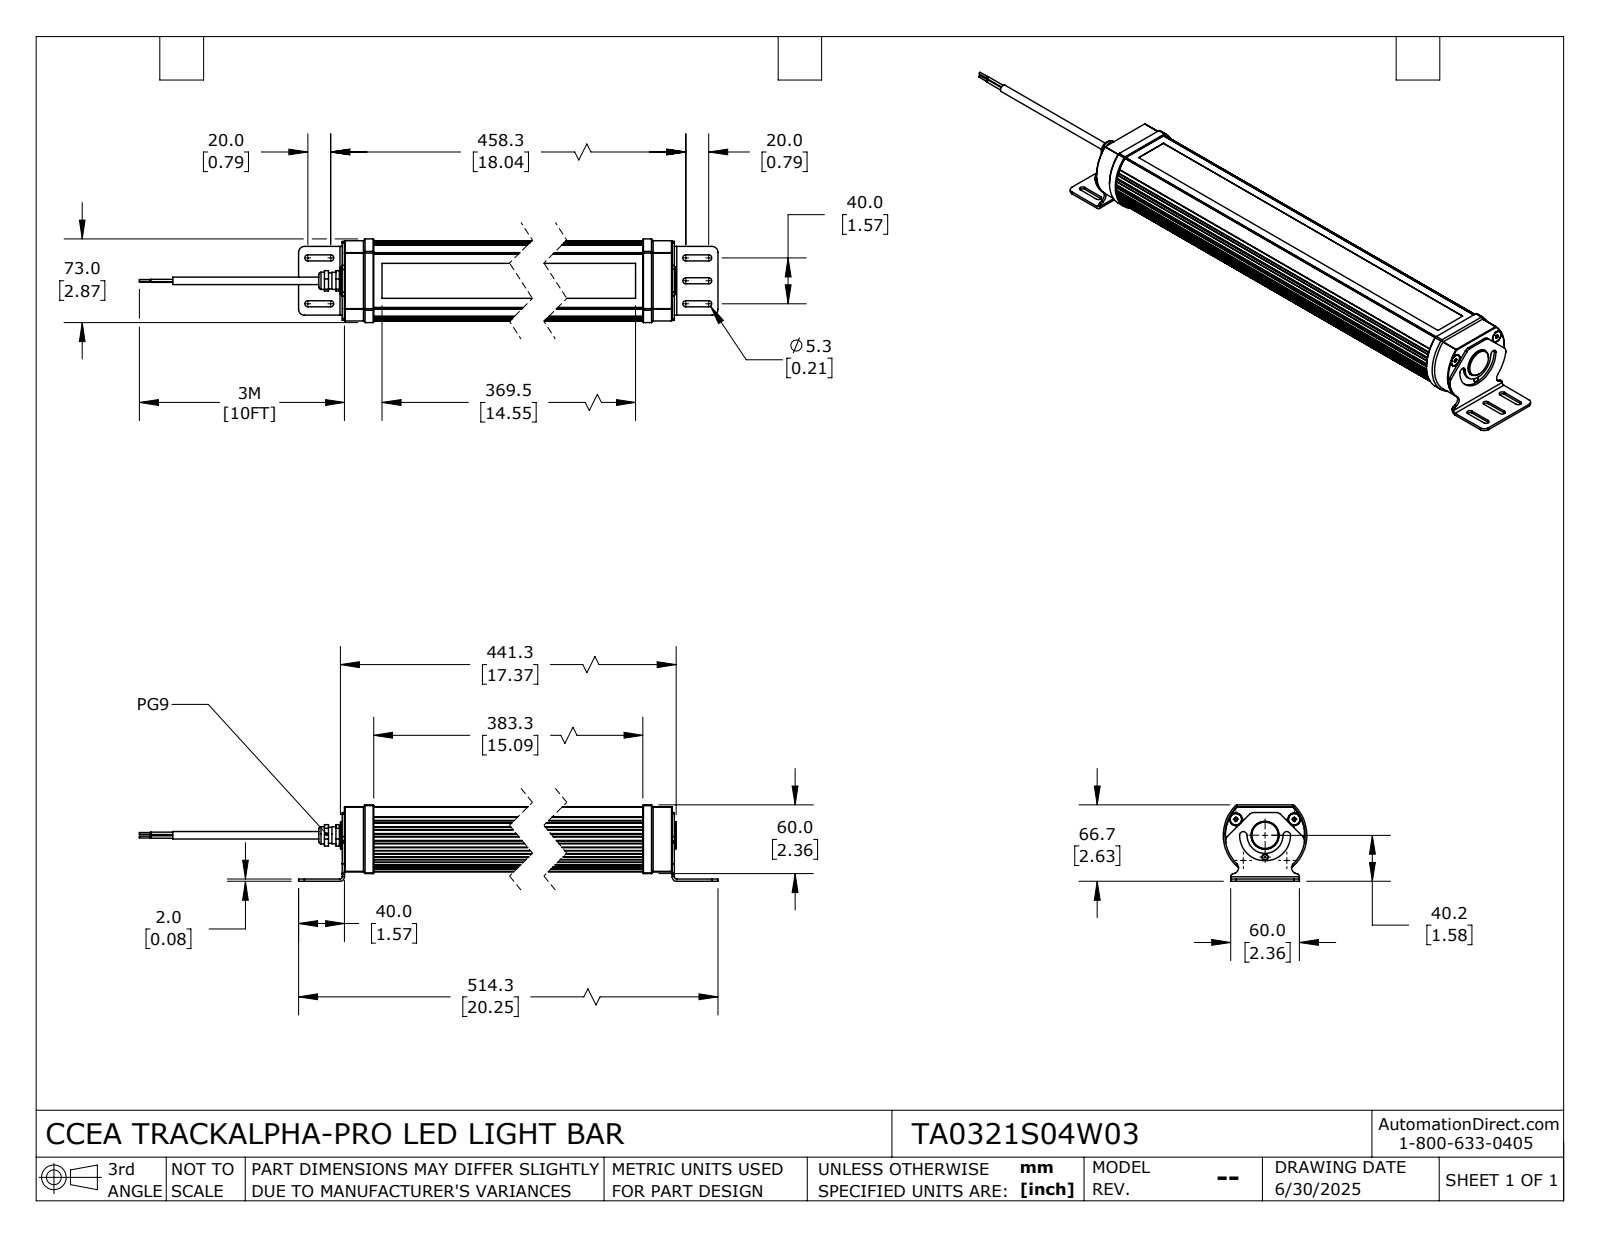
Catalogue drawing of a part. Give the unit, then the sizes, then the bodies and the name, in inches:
Units: inches
Overall size (bounding box): 25.72 × 2.874 × 2.626
Round holes (diameter × count): ⌀0.217 ×4, ⌀0.043 ×2, ⌀0.12 ×2, ⌀0.394 ×2, ⌀0.194 ×1, ⌀0.276 ×1, ⌀0.551 ×1, ⌀0.965 ×1, ⌀1.063 ×1
Round bosses / shafts (diameter × count): ⌀0.394 ×4, ⌀0.197 ×4, ⌀0.118 ×2, ⌀0.082 ×2, ⌀0.067 ×2, ⌀0.063 ×2, ⌀0.039 ×2, ⌀0.945 ×1
Partial cylindrical surfaces — rounded edges, fillets, slot ends (radius × count): R0.02 ×22, R0.012 ×16, R0.197 ×13, R0.104 ×12, R0.059 ×10, R0.073 ×8, R0.079 ×8, R0.028 ×2
Main face-to-face distances: 0.02, 0.197, 2.043, 2.24, 0.217, 2.024, 0.079, 2.242, 0.219, 0.199
Hole centre spacings: 0.334, 0.505, 0.726, 0.757, 0.831, 0.948, 0.992, 1.144
Volume: 90.33 in³ · Surface area: 284.4 in²
Bodies: 3 solids, 695 faces (238 planar, 331 cylindrical, 126 other)
Part name (STEP PRODUCT): TA0321S04W03
STEP written by: SolidWorks 2024 (CONFIG_CONTROL_DESIGN)
